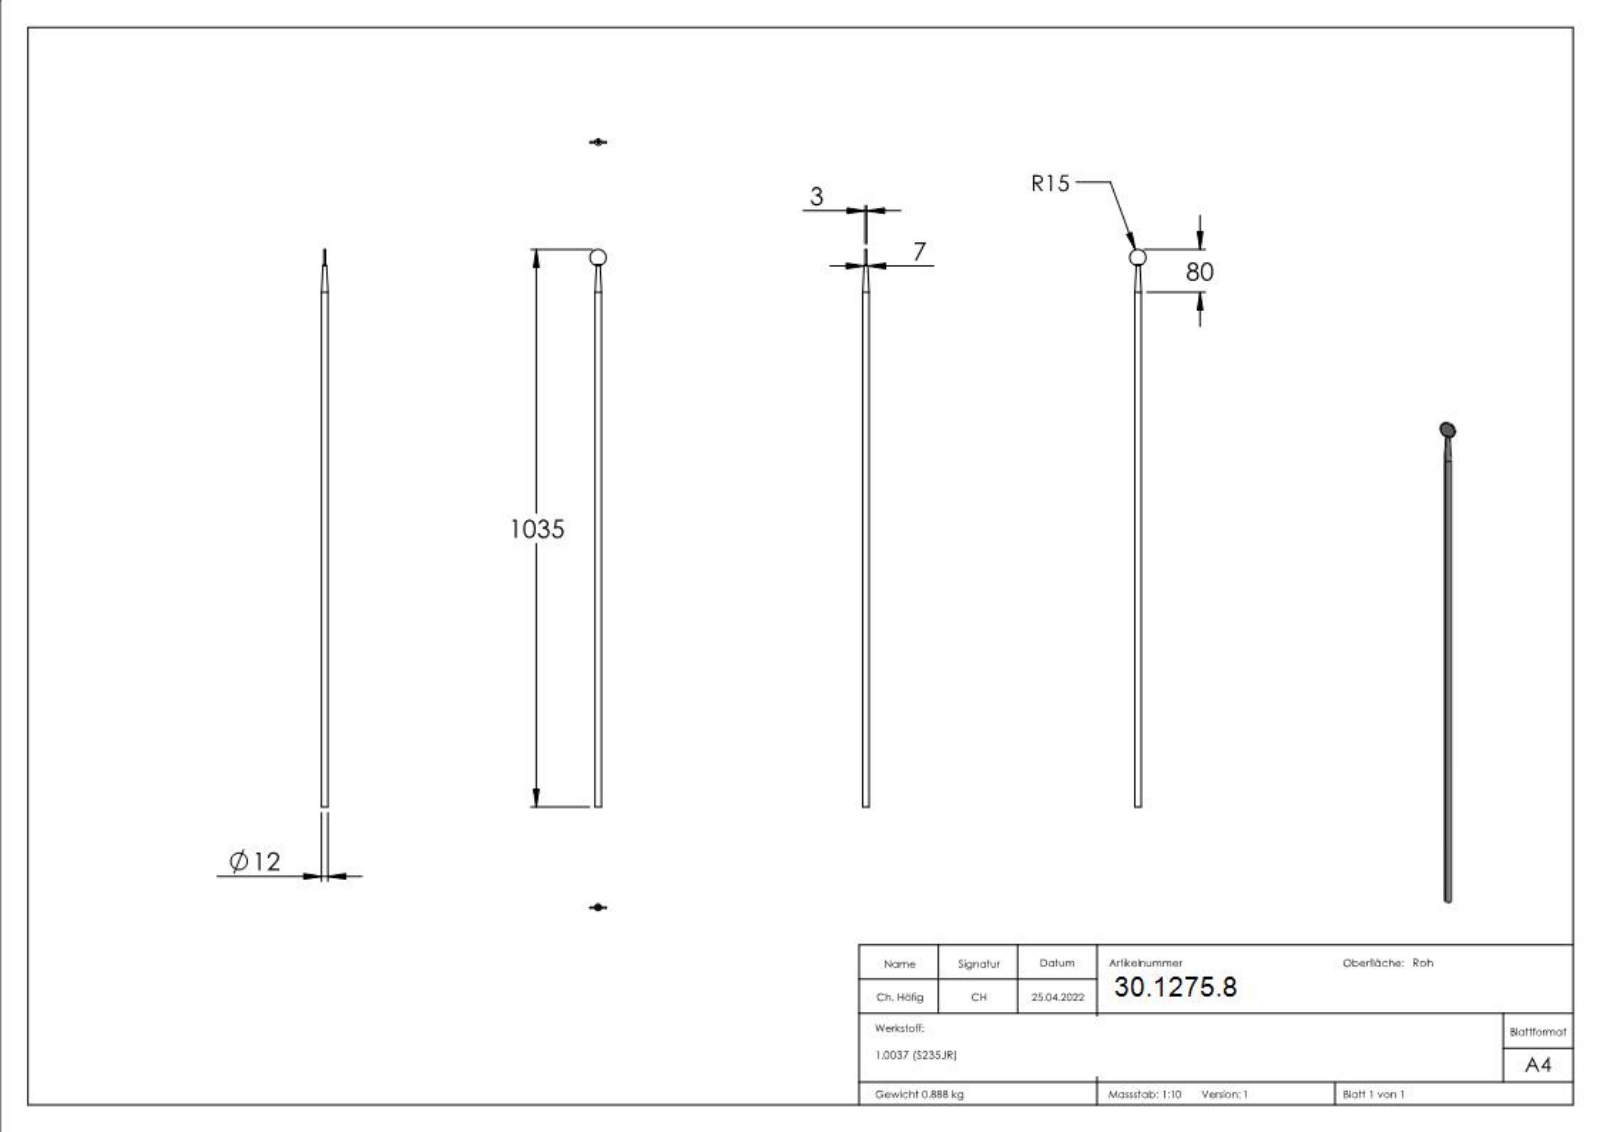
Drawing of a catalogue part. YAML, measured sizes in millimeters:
part_name: "1445"
step_written_by: "SolidWorks 2018 (CONFIG_CONTROL_DESIGN)"
units: millimeters
bodies: {solids: 1, faces: 220, planar: 135, cylindrical: 4, other: 81}
overall_size: [1035, 30, 12]
volume: 113787
surface_area: 39338
round_bosses_or_shafts:
  - {diameter: 30, count: 1}
  - {diameter: 12, count: 1}
partial_cylinders:
  - {radius: 2, count: 2}
face_to_face_distances: [3, 0.5, 2.21, 1.62, 0.34, 2.2, 2.45, 2.24, 0.83, 1.87]
